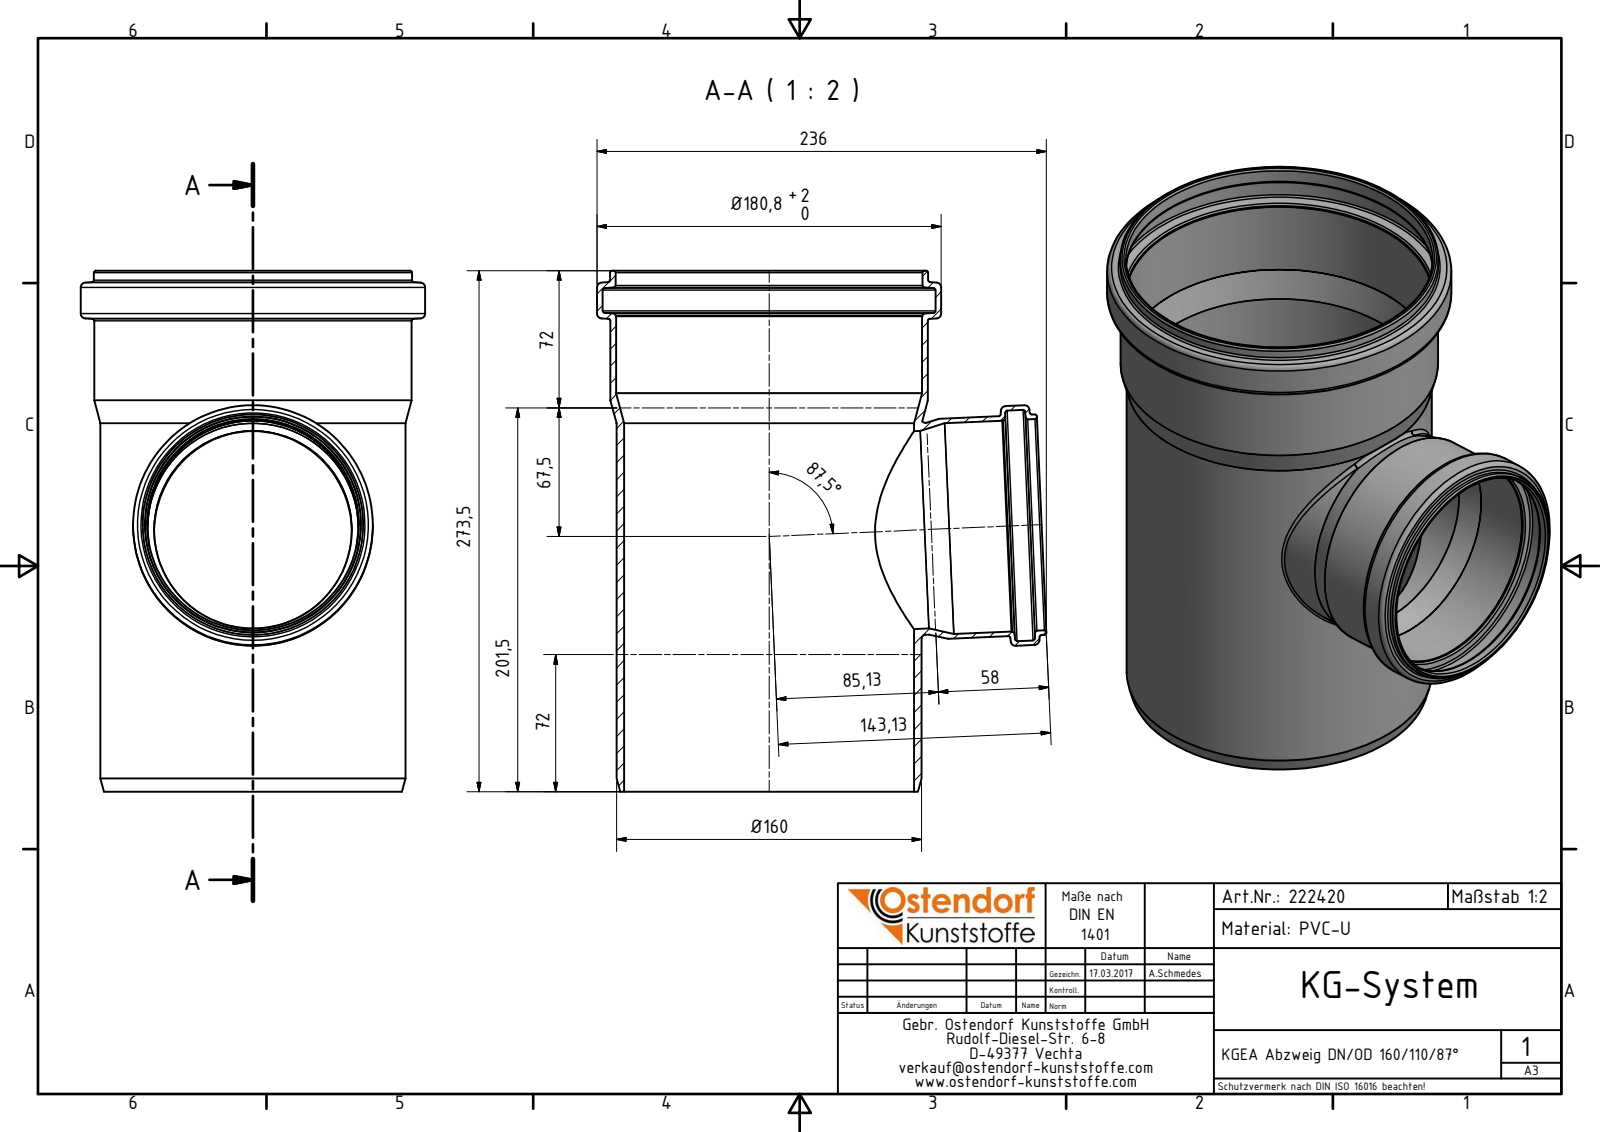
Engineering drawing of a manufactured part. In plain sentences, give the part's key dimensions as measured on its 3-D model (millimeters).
The part is named "222420 KGEA Abzweig DN_OD 160_110_87°". Its 3-D file was written by "Autodesk Inventor 2016 (AUTOMOTIVE_DESIGN)". It is 1 solid with 70 faces: 5 planar, 18 cylindrical and 47 other. Overall it measures 273.5 by 236 by 180.8 millimeters. Its volume is 568 399 cubic millimeters and its surface area 328 223 square millimeters. Round holes: 2 of diameter 111, 1 of diameter 103.8, 1 of diameter 110.7, 1 of diameter 121.1, 1 of diameter 152.2, 1 of diameter 160.7, 1 of diameter 161.1, 1 of diameter 174.8. Round bosses or shafts: 1 of diameter 180.8, 1 of diameter 167.1, 1 of diameter 166.7, 1 of diameter 160.2, 1 of diameter 125.9, 1 of diameter 115.8, 1 of diameter 115.5, 1 of diameter 110.2. The main face-to-face distances are 273.5, 249.53, 23.97, 18.21.
